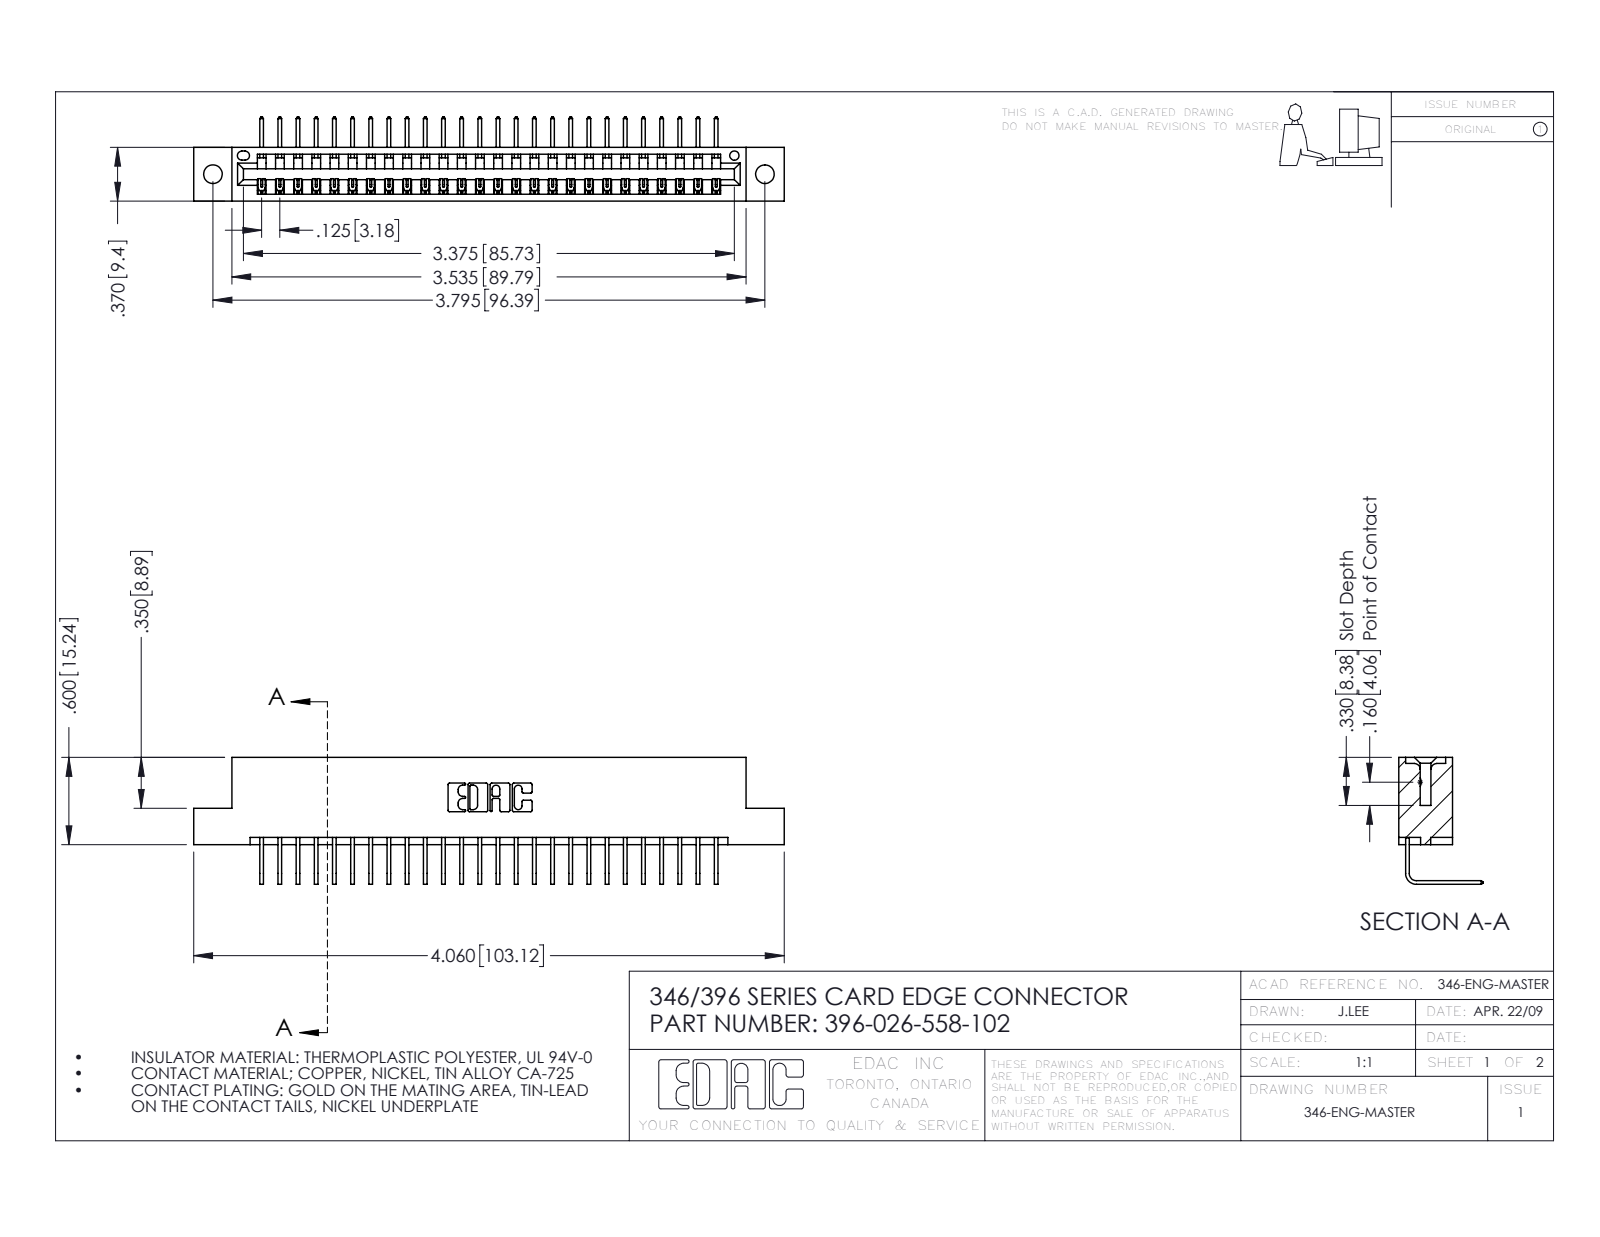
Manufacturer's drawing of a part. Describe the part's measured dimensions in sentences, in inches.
The part is named "346 Part_Flush Mounting Lugs - 0.128 Dia; 396-026-558-102; 345-292-001_558 Tail - 2". Its 3-D file was written by "SolidWorks 2016 (CONFIG_CONTROL_DESIGN)". It is 27 solids with 1682 faces: 1168 planar, 514 cylindrical and 0 other. Overall it measures 4.06 by 0.873 by 0.58 inches. Its volume is 0.599 cubic inches and its surface area 19.12 square inches. Round holes: 2 of diameter 0.128, 1 of diameter 0.064. Partial cylindrical surfaces (rounded edges, fillets, slot ends): 52 of radius 0.006, 22 of radius 0.01, 6 of radius 0.007, 6 of radius 0.031, 3 of radius 0.026, 2 of radius 0.031, 2 of radius 0.04, 1 of radius 0.014. The main face-to-face distances are 0.322, 0.048, 0.37, 0.25, 0.298, 0.025, 0.072, 0.148, 0.222, 0.1. The hole center spacings are 0.246, 3.587, 3.795.
